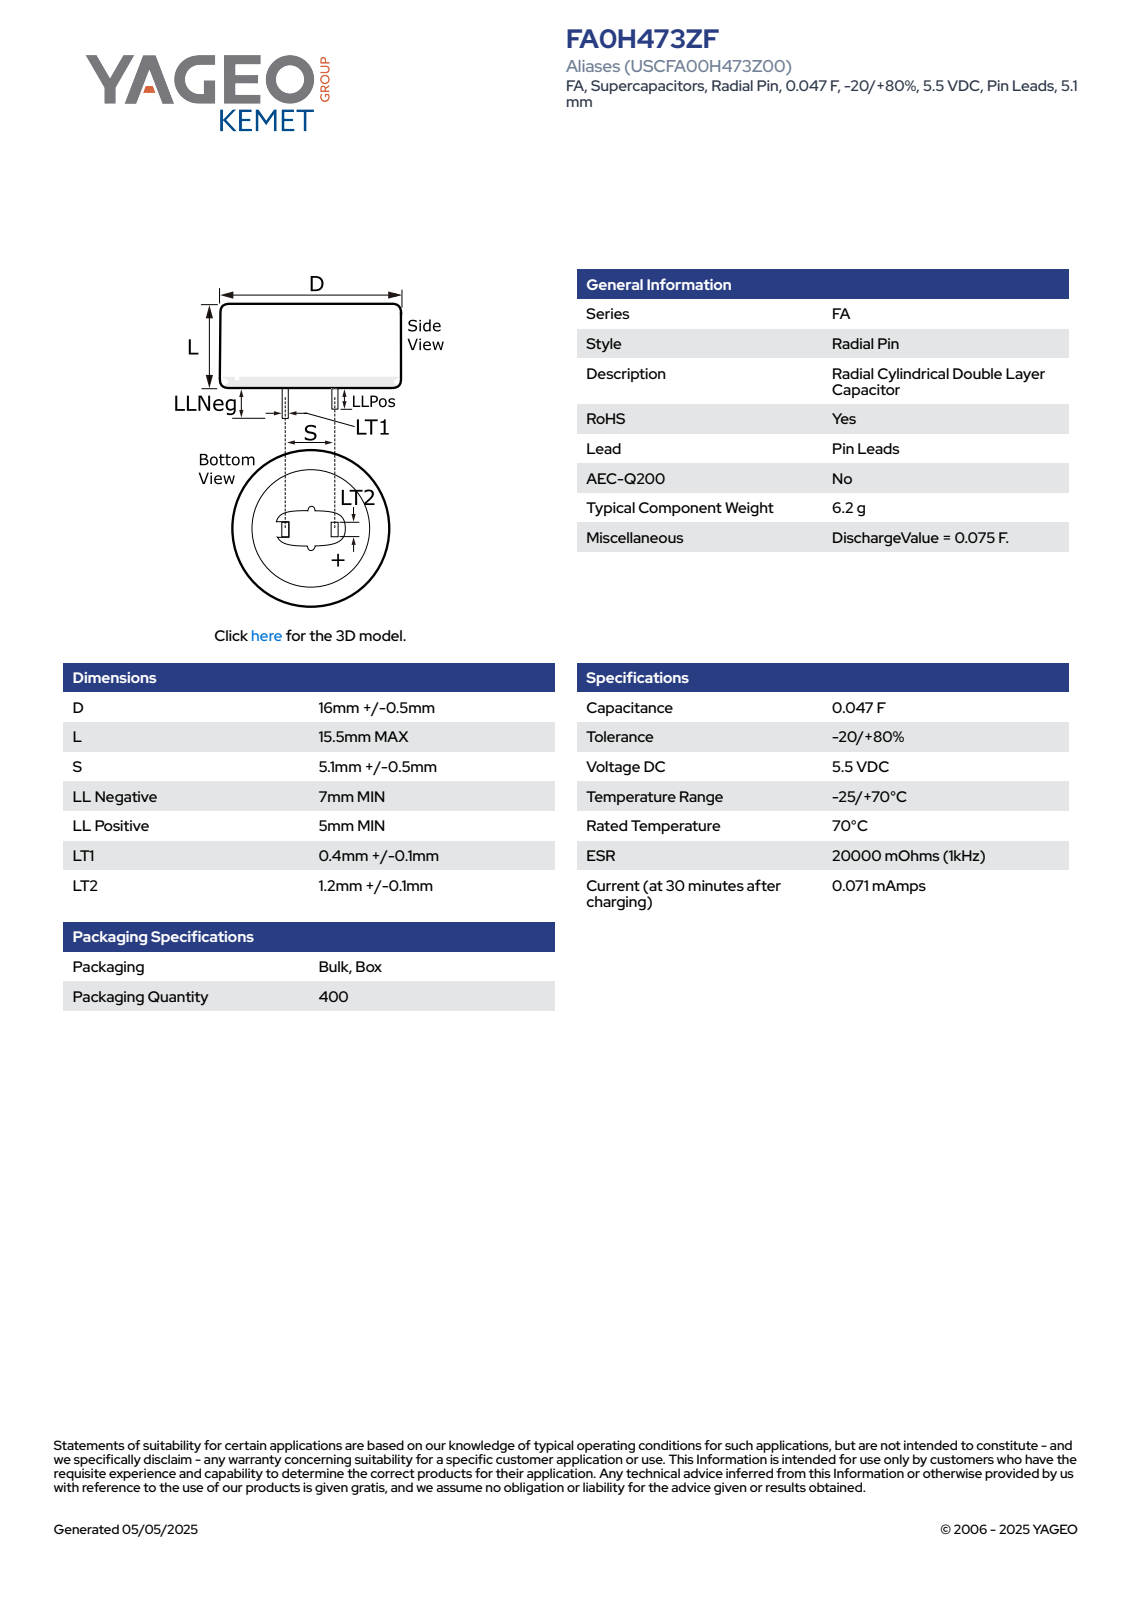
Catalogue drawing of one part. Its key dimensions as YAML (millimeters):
part_name: "CDR_LPLLN_D16.5L15.5S5.1LLNEG7LLPOS5LT10.5LT21.3"
step_written_by: "SolidWorks 2014 (AUTOMOTIVE_DESIGN)"
units: millimeters
bodies: {solids: 1, faces: 78, planar: 70, cylindrical: 4, other: 4}
overall_size: [22.5, 16.5, 16.5]
volume: 3301
surface_area: 1230
round_bosses_or_shafts:
  - {diameter: 16.5, count: 1}
partial_cylinders:
  - {radius: 8.26, count: 1}
face_to_face_distances: [15.5, 0.5, 5.1, 15.49, 5.6, 4.6, 1.3, 2, 7, 22.49]
